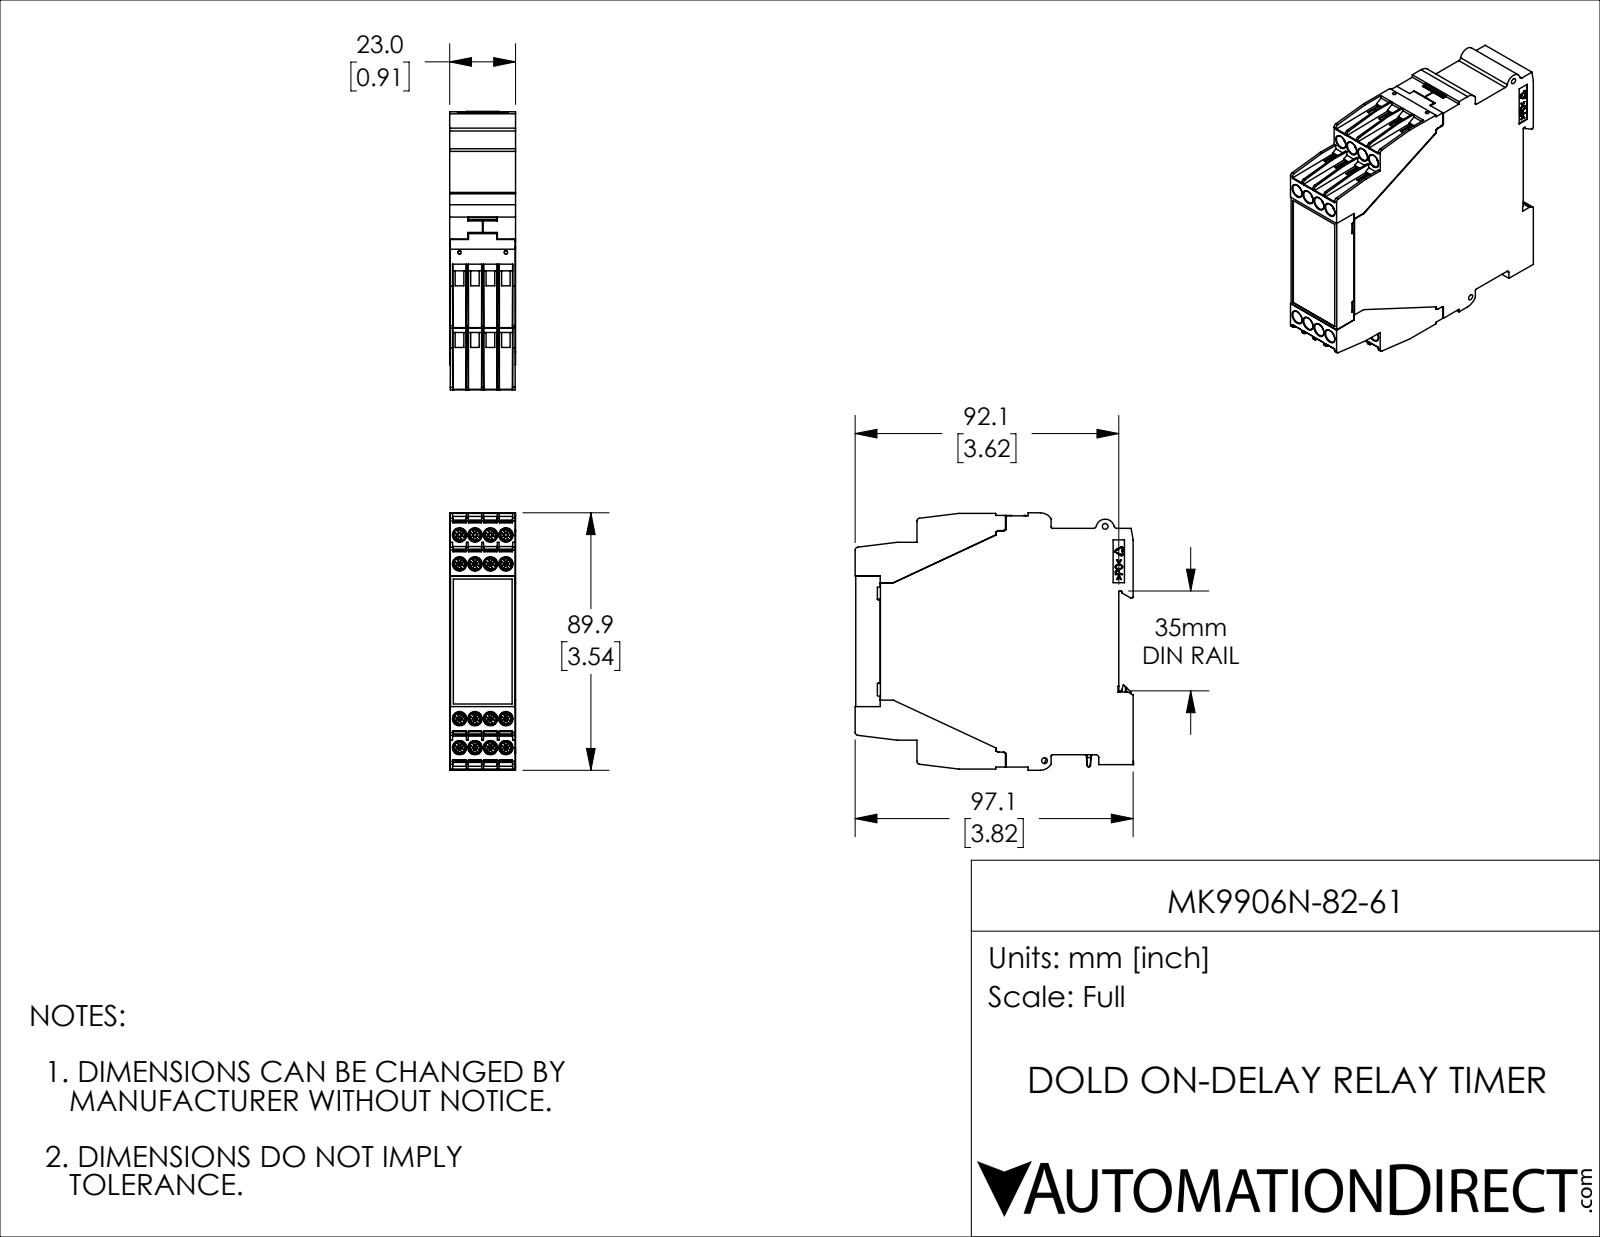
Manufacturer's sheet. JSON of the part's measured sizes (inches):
{"part_name": "MK9906N-82-61", "step_written_by": "SolidWorks 2019 (CONFIG_CONTROL_DESIGN)", "units": "inches", "bodies": {"solids": 1, "faces": 1833, "planar": 1399, "cylindrical": 295, "other": 139}, "overall_size": [3.827, 3.537, 0.906], "volume_in3": 10.38, "surface_area_in2": 51.14, "round_holes": [[0.181, 16], [0.079, 3], [0.047, 2], [0.079, 2]], "round_bosses_or_shafts": [[0.173, 12], [0.087, 1]], "partial_cylinders_radius": [[0.012, 50], [0.02, 30], [0.039, 23], [0.008, 7], [0.006, 6], [0.014, 6], [0.087, 4], [0.174, 2]], "face_to_face_distances": [0.906, 0.9, 0.026, 0.864, 0.894, 0.035, 0.839, 0.031, 0.874, 0.868], "hole_center_spacings": [0.213, 0.451, 2.535, 0.398, 0.425, 0.582, 2.526, 2.561]}
